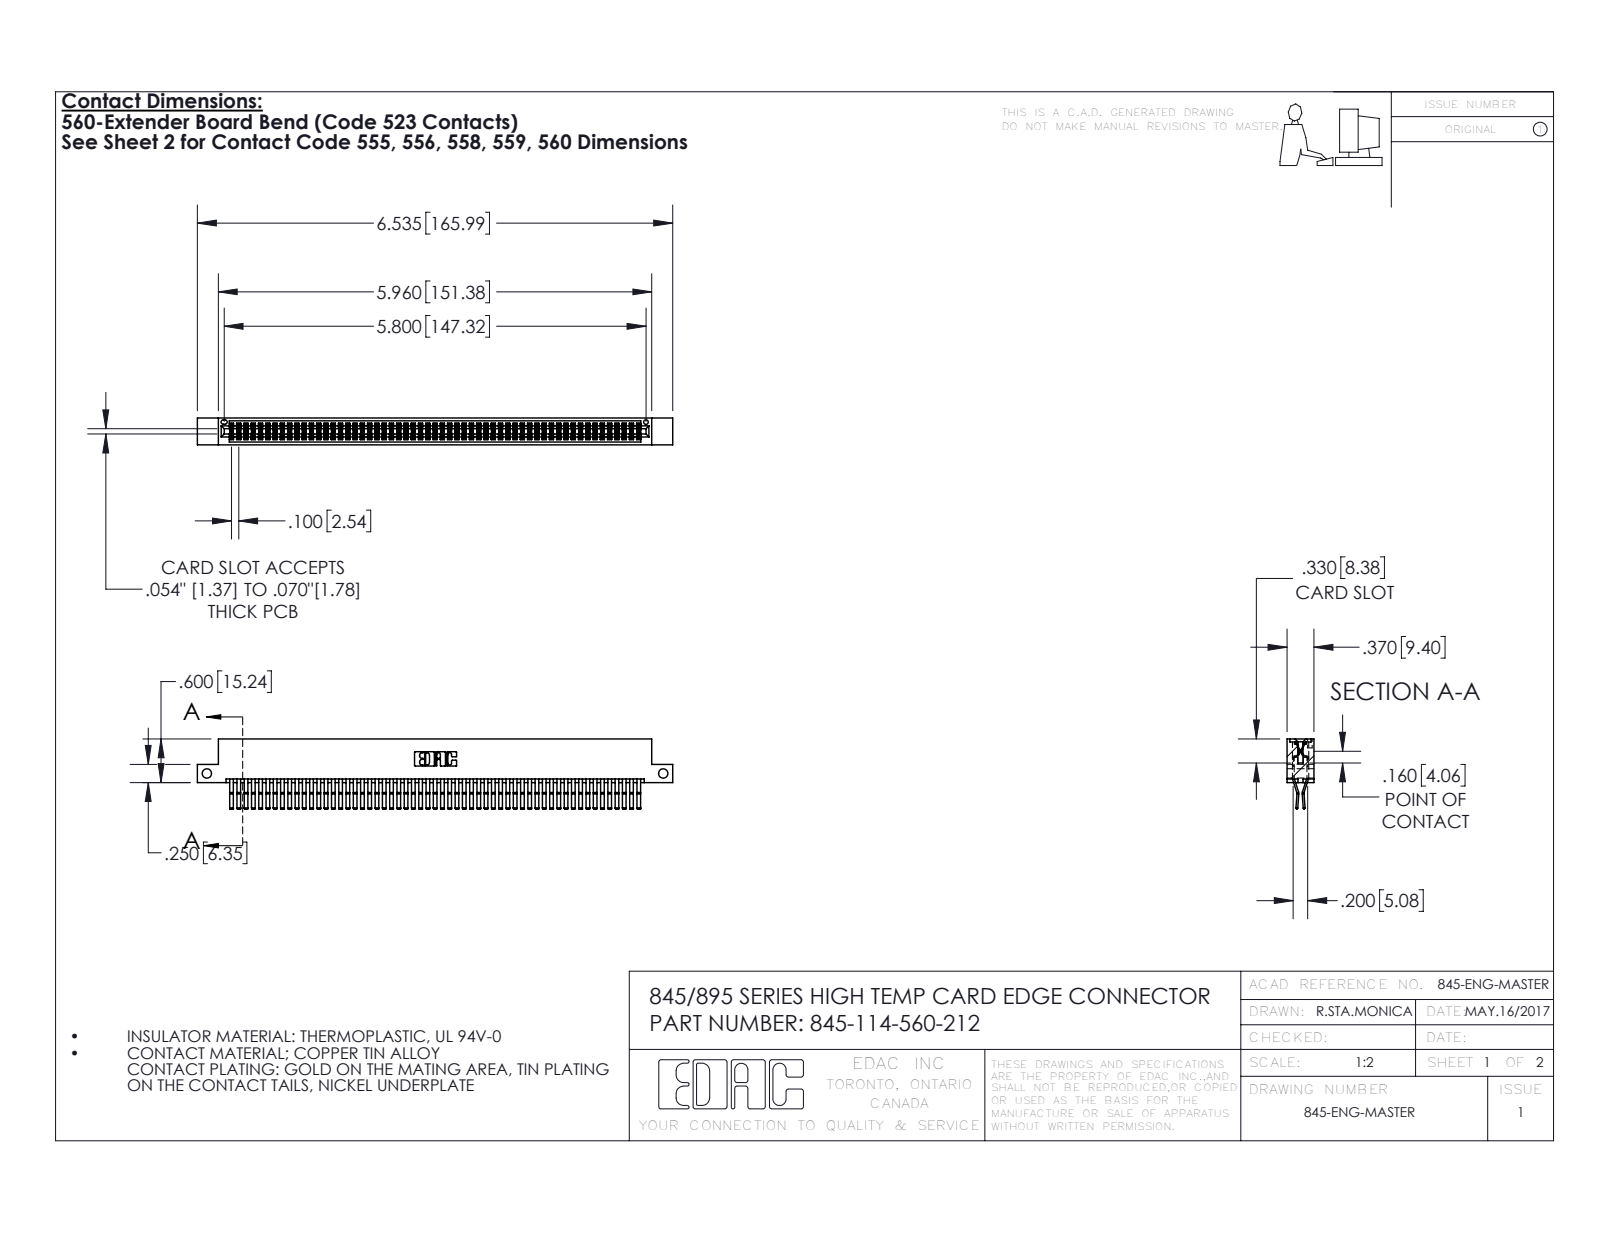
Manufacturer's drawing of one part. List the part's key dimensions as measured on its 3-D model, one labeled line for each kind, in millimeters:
Part name (STEP PRODUCT): 345-114-560-212; 345-292-001_560 Tail; 345 Part_Flush Mounting Lugs - Side Mount
STEP written by: SolidWorks 2016 (CONFIG_CONTROL_DESIGN)
Units: millimetres
Bodies: 115 solids, 6054 faces (3842 planar, 2212 cylindrical, 0 other)
Overall size (bounding box): 166 × 24.4 × 9.4
Volume: 16 930 mm³ · Surface area: 27 090 mm²
Round holes (diameter × count): ⌀3.3 ×2, ⌀1.6 ×1
Partial cylindrical surfaces — rounded edges, fillets, slot ends (radius × count): R0.2 ×171, R0.3 ×22, R0.2 ×6, R0.8 ×6, R0.7 ×3, R0.3 ×2, R0.4 ×2, R0.5 ×2
Main face-to-face distances: 0.6, 7.6, 1.8, 9.4, 5.1, 2.5, 6.9, 5.7, 4.4, 3.8
Hole centre spacings: 159.4
